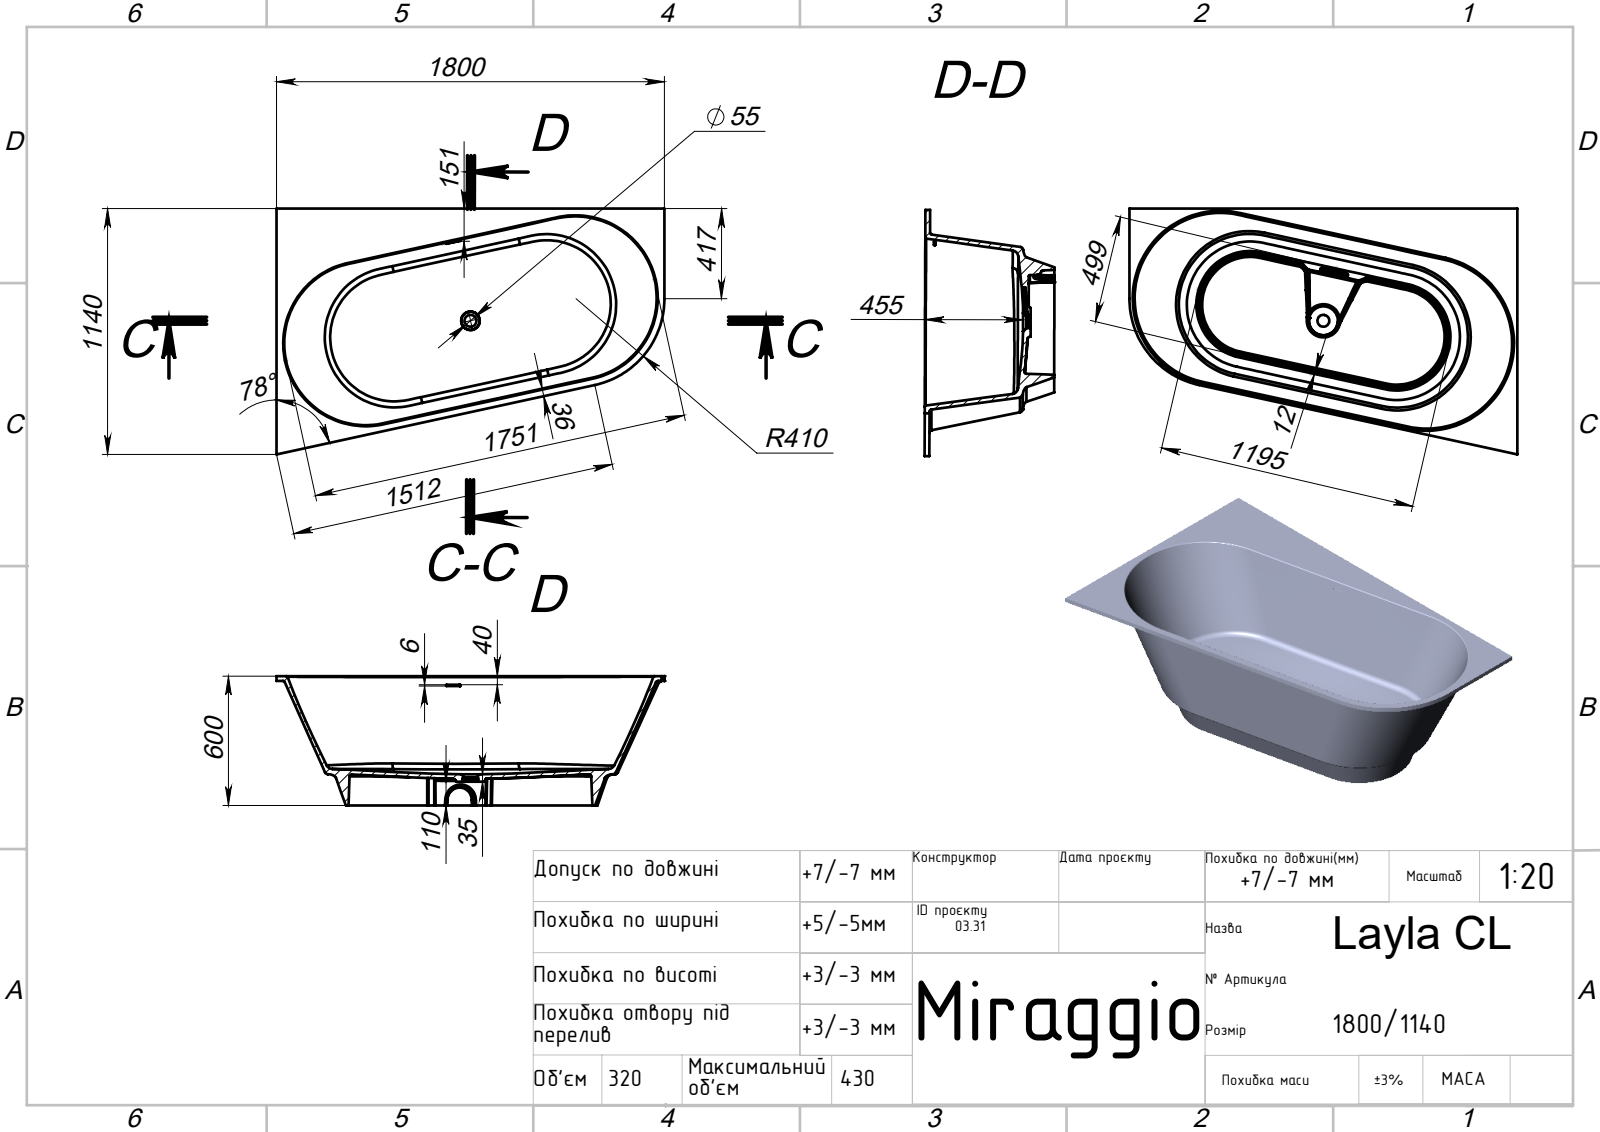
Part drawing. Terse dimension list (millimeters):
name: Layla CL
written by: SolidWorks 2020 (AUTOMOTIVE_DESIGN)
unit: mm
bodies: 1 solid, 125 faces (28 planar, 19 cylindrical, 78 other)
size: 2001.85 × 1113.86 × 600
volume: 75 780 000 mm³; area: 6 912 000 mm²
holes: 1× ⌀55
rounds: 4× R10, 3× R5, 2× R3, 1× R37, 1× R46, 1× R62.5, 1× R198.58, 1× R237.27
face distances: 22, 578, 600, 119, 459, 481, 110, 9, 468, 490
